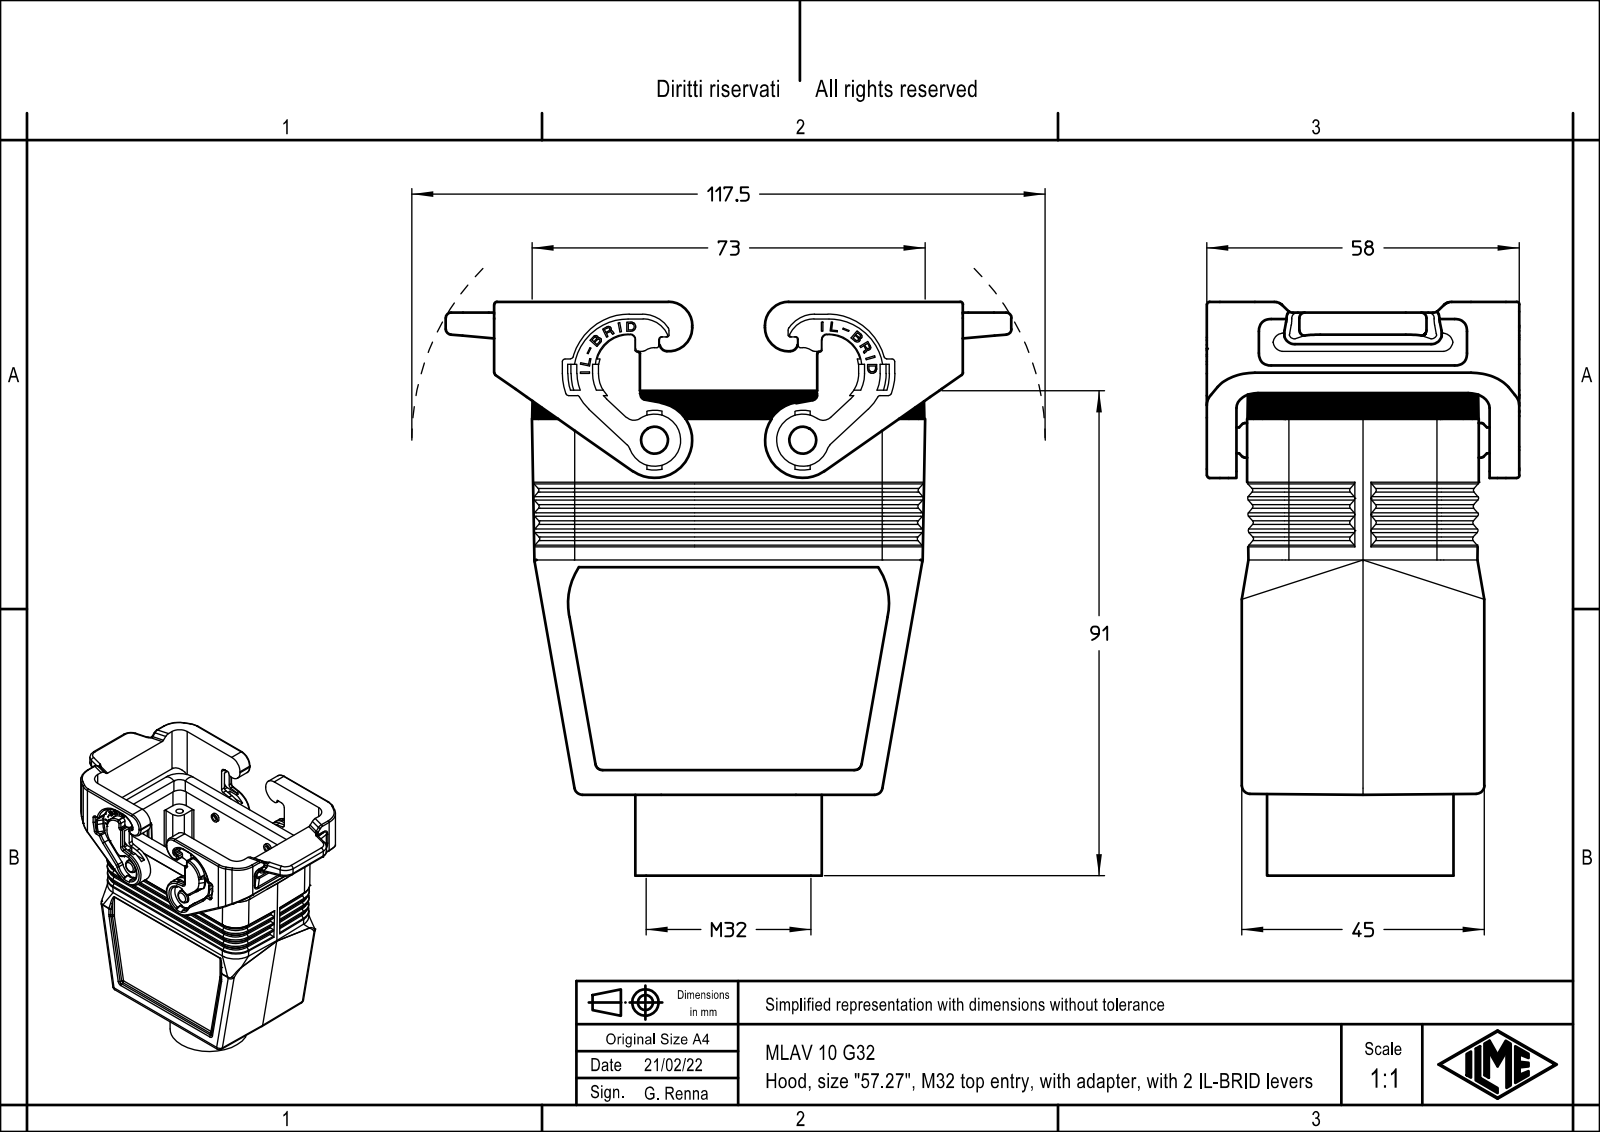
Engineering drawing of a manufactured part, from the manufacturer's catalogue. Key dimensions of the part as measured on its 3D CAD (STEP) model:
Part name (STEP PRODUCT): MLAV_10_G32
STEP written by: Creo Elements/Direct Modeling 20.1B 02-Apr-2019 (C) Parametric Technology GmbH (AUTOMOTIVE_DESIGN)
Units: millimetres
Bodies: 1 solid, 1489 faces (960 planar, 337 cylindrical, 192 other)
Overall size (bounding box): 107.45 × 105 × 58
Volume: 100 725 mm³ · Surface area: 53 318 mm²
Round holes (diameter × count): ⌀2.75 ×4, ⌀27 ×1, ⌀32 ×1
Round bosses / shafts (diameter × count): ⌀6.8 ×2, ⌀4.8 ×2, ⌀36 ×1
Partial cylindrical surfaces — rounded edges, fillets, slot ends (radius × count): R1 ×54, R0.5 ×43, R3 ×20, R7 ×16, R0.33 ×15, R1.5 ×14, R0.3 ×8, R2 ×8
Main face-to-face distances: 39.25, 2, 3.75, 5.75, 1, 45, 41.25, 43, 4.75, 40.25
Hole centre spacings: 31.54, 27, 57, 63.07
